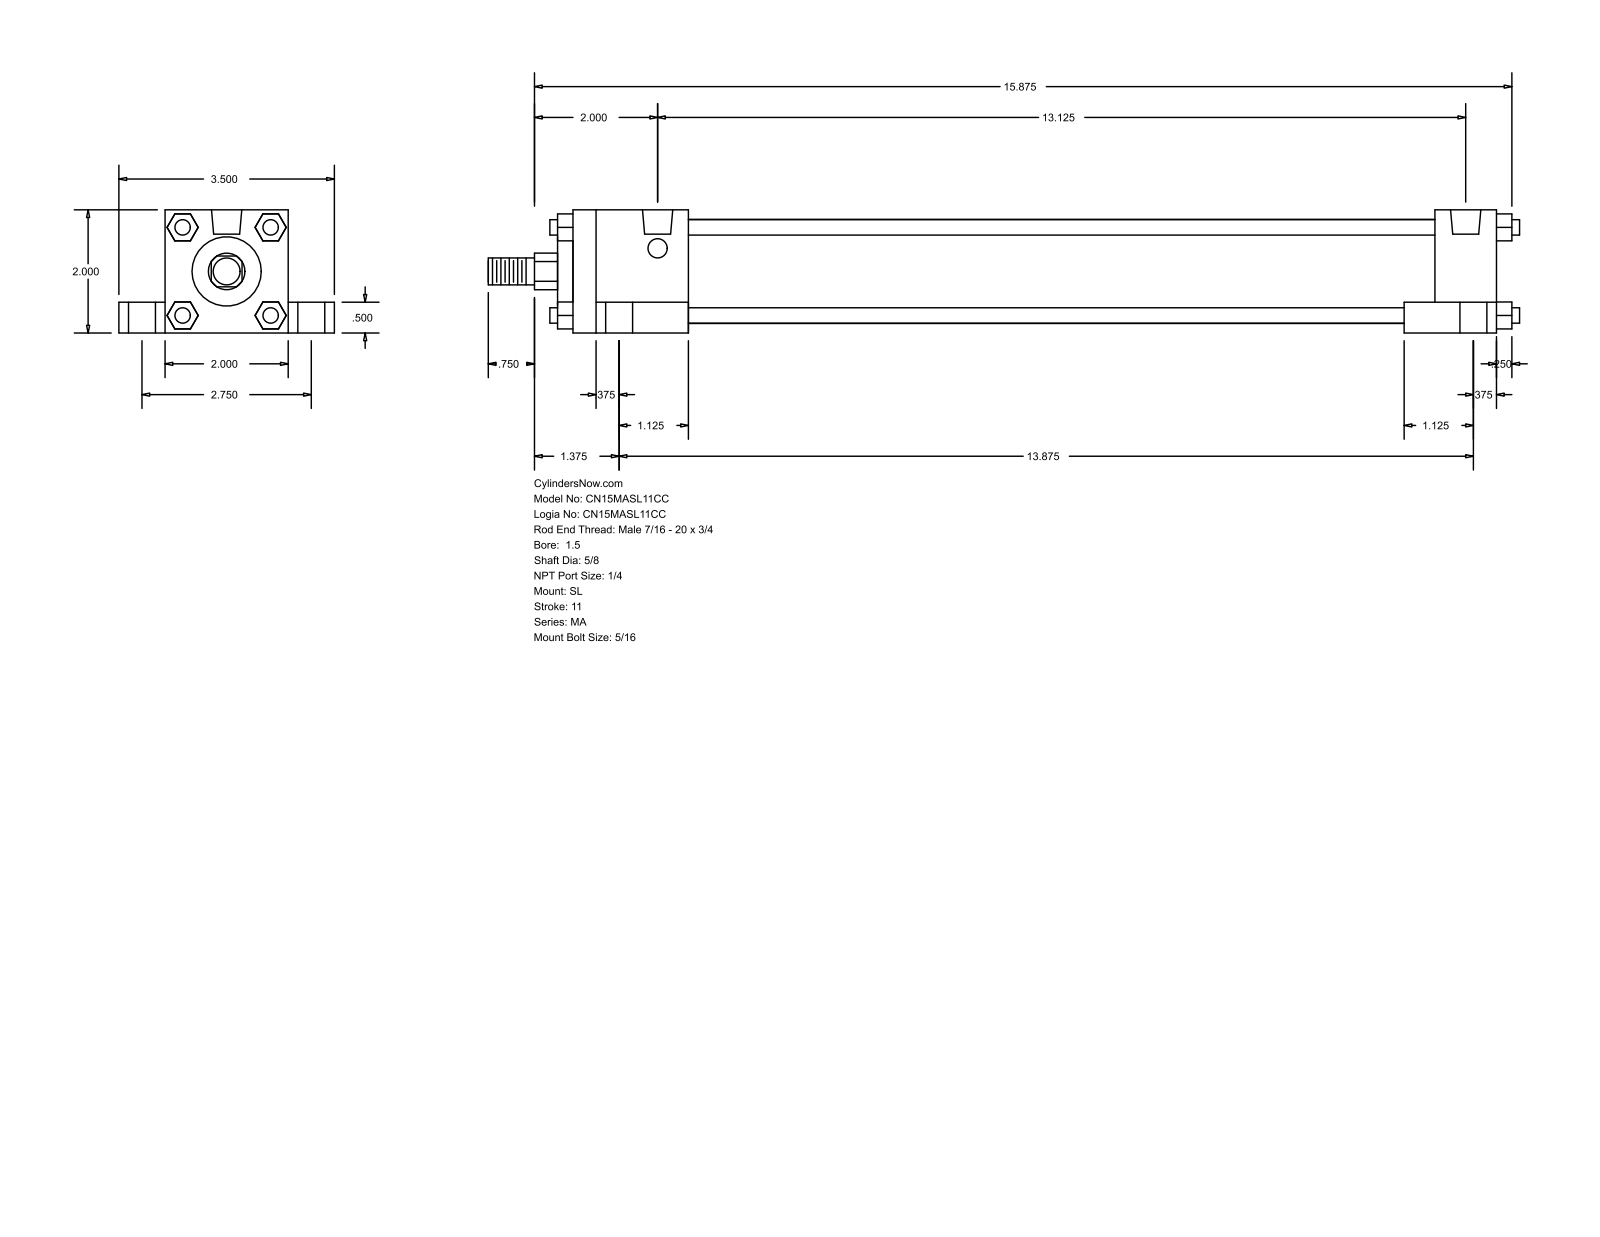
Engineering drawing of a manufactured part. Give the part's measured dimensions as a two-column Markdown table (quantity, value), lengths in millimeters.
| quantity | value |
| --- | --- |
| part name | MA_SL__0150_0.625 |
| STEP written by | GSSL Pune (CONFIG_CONTROL_DESIGN) |
| units | millimeters |
| bodies | 0 solids, 148 faces (112 planar, 36 cylindrical, 0 other) |
| overall size | 425.45 × 88.9 × 50.8 |
| round holes (diameter × count) | 7.94 × 4, 11.11 × 4, 17.46 × 4, 12.49 × 2 |
| round bosses / shafts (diameter × count) | 6.35 × 4, 42.93 × 1, 28.57 × 1, 15.88 × 1, 11.11 × 1 |
| partial cylindrical surfaces (radius × count) | 7.54 × 1 |
| main face-to-face distances | 50.8, 19.05, 38.1, 381, 69.85, 12.7, 9.52, 25.4, 6.35, 387.35 |
| hole center spacings | 35.06, 38.36, 69.84, 333.38, 338.36, 351, 352.43, 359.28 |
